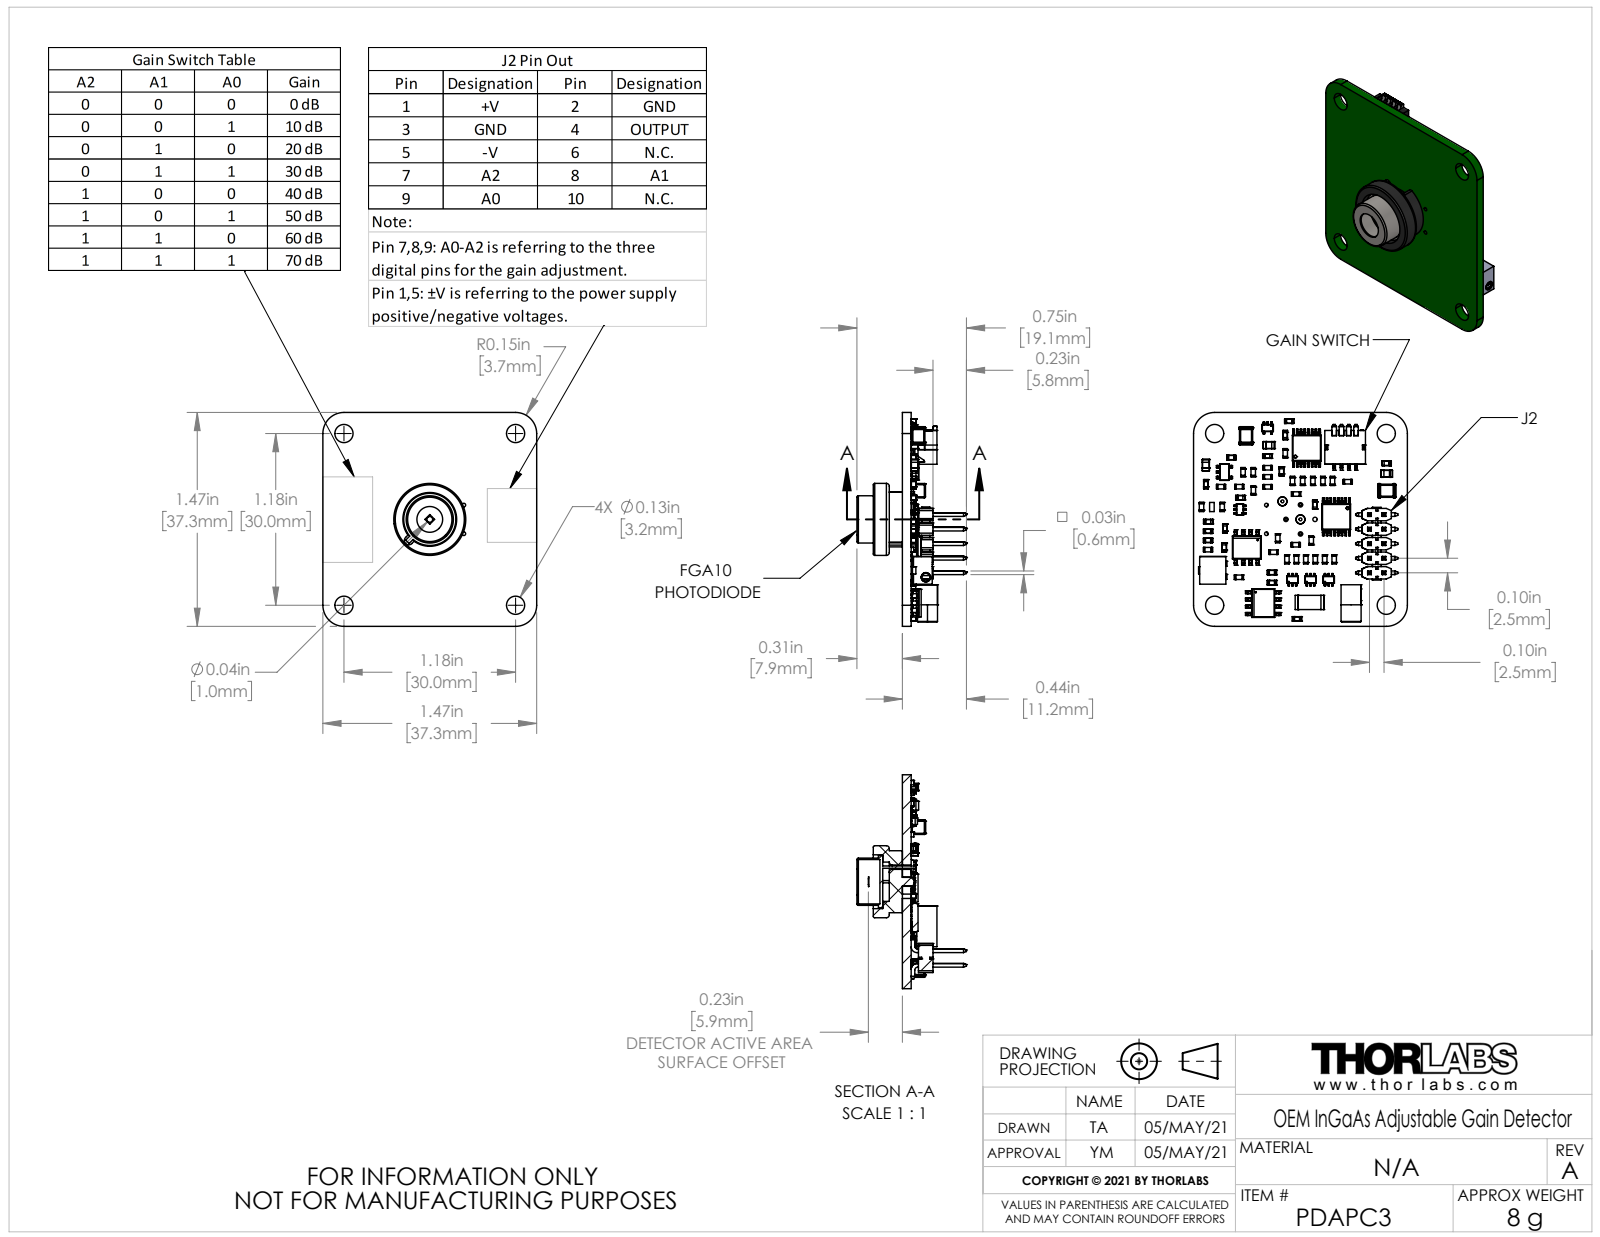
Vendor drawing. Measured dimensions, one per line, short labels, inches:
name: TTN239792-E0W
written by: SolidWorks 2018 (AUTOMOTIVE_DESIGN)
unit: in
bodies: 76 solids, 4196 faces (2911 planar, 1043 cylindrical, 242 other)
size: 1.47 × 1.47 × 0.753
volume: 0.194 in³; area: 9.127 in²
holes: 5× ⌀0.008, 4× ⌀0.03, 4× ⌀0.125, 2× ⌀0.02, 2× ⌀0.025, 2× ⌀0.063, 1× ⌀0.04, 1× ⌀0.047, 1× ⌀0.064, 1× ⌀0.095, 1× ⌀0.114, 1× ⌀0.119
bosses: 3× ⌀0.06, 3× ⌀0.016, 1× ⌀0.495, 1× ⌀0.358, 1× ⌀0.325, 1× ⌀0.138, 1× ⌀0.089, 1× ⌀0.04
rounds: 59× R0.004, 54× R0.008, 10× R0.01, 10× R0.02, 8× R0.014, 6× R0.01, 4× R0.005, 4× R0.145
face distances: 0.06, 0.1, 0.2, 0.195, 0.135, 0.045, 1.47, 0.264, 0.065, 0.103
hole spacings: 0.1, 0.141, 0.2, 0.224, 0.544, 0.3, 0.316, 0.479
